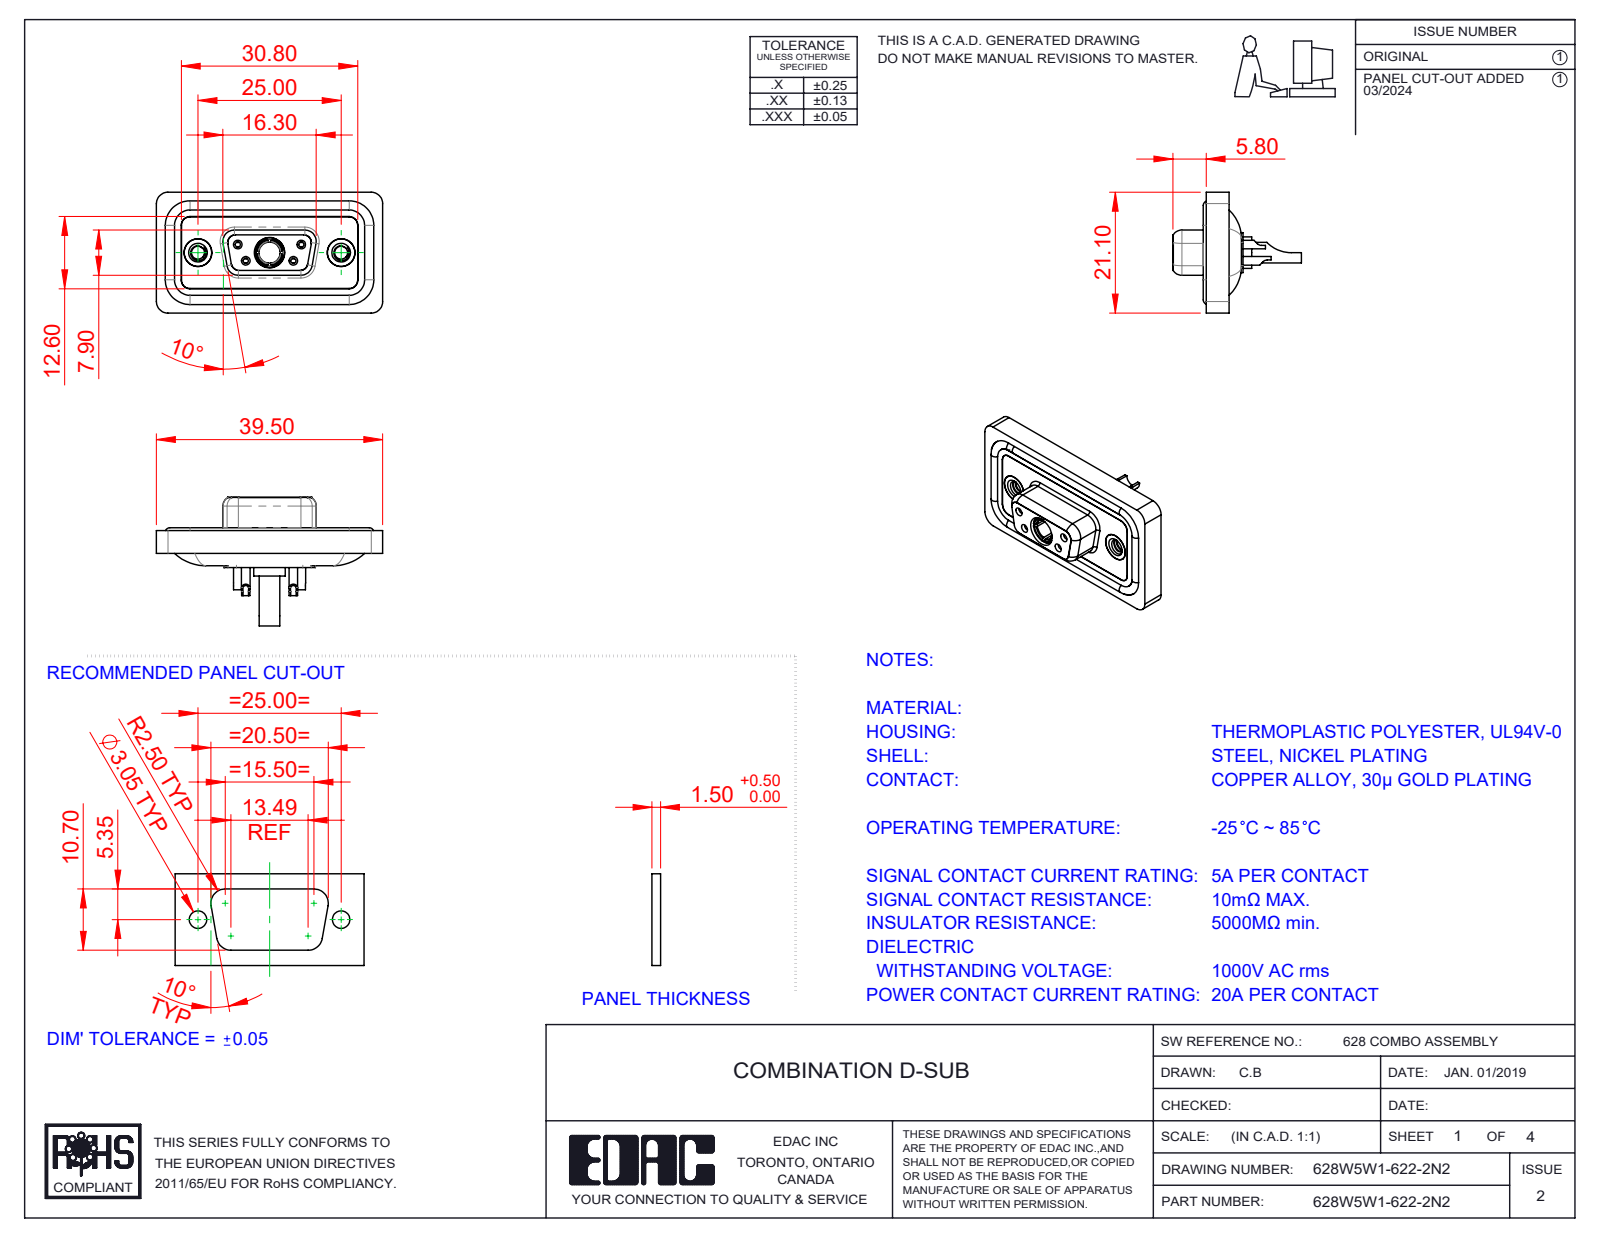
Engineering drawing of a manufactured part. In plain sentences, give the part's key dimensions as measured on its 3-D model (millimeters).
The part is named "628Combo Threaded Rivet_2; Power Socket_20A SC; 628Combo Contact Row 1_22; 628Combo Contact Row 2_22 (+5 more)". Its 3-D file was written by "SolidWorks 2023 (CONFIG_CONTROL_DESIGN)". It is 13 solids with 686 faces: 205 planar, 298 cylindrical and 183 other. Overall it measures 39.5 by 22.45 by 21.1 millimeters. Its volume is 4 788 cubic millimeters and its surface area 7 760 square millimeters. Round holes: 4 of diameter 0.9, 4 of diameter 1, 4 of diameter 1.1, 4 of diameter 1.5, 4 of diameter 2, 3 of diameter 4.85, 2 of diameter 1.6, 2 of diameter 1.7, 2 of diameter 2.26, 2 of diameter 4, 2 of diameter 4.05, 2 of diameter 5. Round bosses or shafts: 6 of diameter 1.6, 4 of diameter 2.2, 2 of diameter 4.95, 2 of diameter 4.8, 1 of diameter 5.5, 1 of diameter 5.2, 1 of diameter 4.96, 1 of diameter 4.75. Partial cylindrical surfaces (rounded edges, fillets, slot ends): 22 of radius 1.5, 18 of radius 2, 8 of radius 1.35, 8 of radius 1.6, 6 of radius 1, 4 of radius 0.25, 4 of radius 0.5, 4 of radius 0.6. The main face-to-face distances are 0.4, 2.9, 1.1, 1.8, 1.6, 0.5, 5.65, 7.45, 5.35, 3.6. The hole center spacings are 3.16, 5.72, 7.1, 12.5, 18.1, 4.39, 4.4, 8.31.
